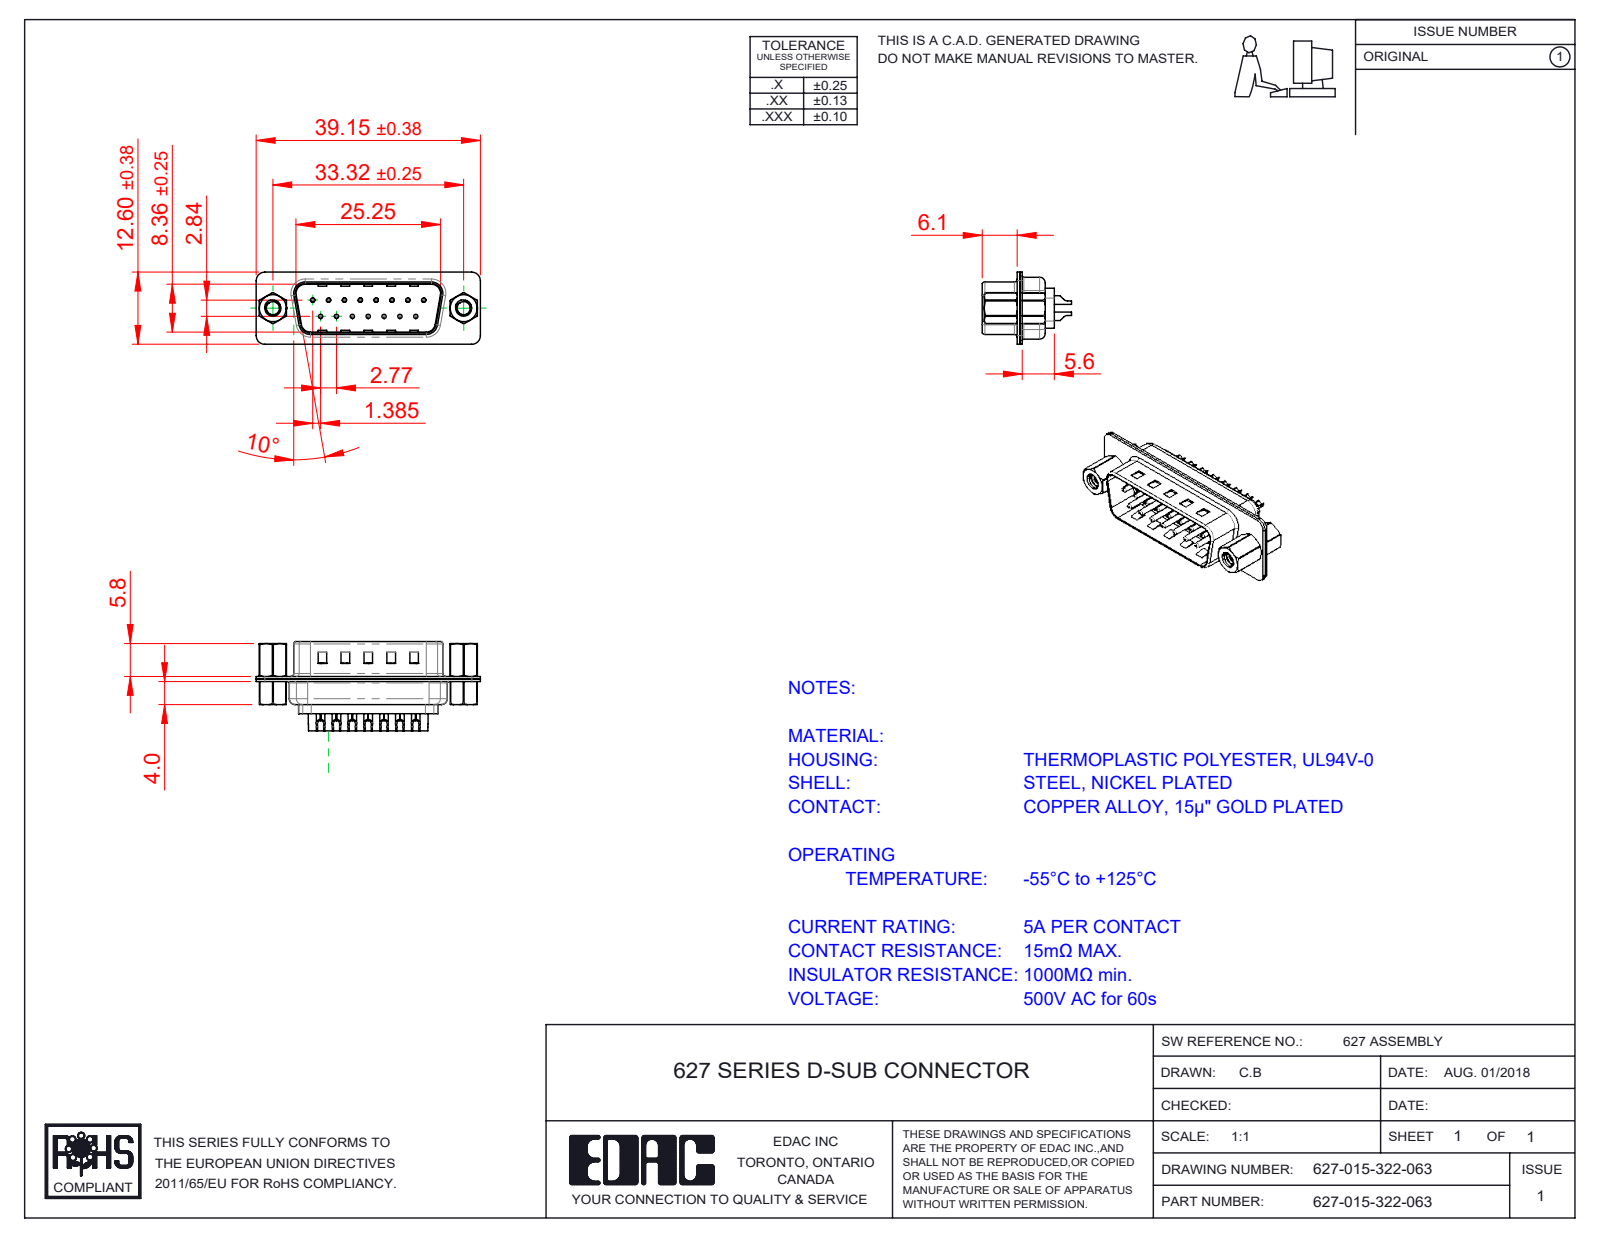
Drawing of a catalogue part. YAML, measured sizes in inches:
part_name: "627-015-322-063; 627 4-40 Threaded Rivet; 627 Contact Row 2_22L; 627 Housing_15 LP (+4 more)"
step_written_by: "SolidWorks 2020 (CONFIG_CONTROL_DESIGN)"
units: inches
bodies: {solids: 22, faces: 1422, planar: 371, cylindrical: 638, other: 413}
overall_size: [1.541, 0.604, 0.496]
volume: 0.125
surface_area: 9.137
round_holes:
  - {diameter: 0.014, count: 15}
  - {diameter: 0.043, count: 15}
  - {diameter: 0.063, count: 15}
  - {diameter: 0.089, count: 2}
  - {diameter: 0.09, count: 2}
  - {diameter: 0.157, count: 2}
  - {diameter: 0.189, count: 2}
round_bosses_or_shafts:
  - {diameter: 0.079, count: 15}
  - {diameter: 0.059, count: 15}
  - {diameter: 0.03, count: 15}
  - {diameter: 0.197, count: 2}
  - {diameter: 0.193, count: 2}
  - {diameter: 0.11, count: 2}
partial_cylinders:
  - {radius: 0.059, count: 16}
  - {radius: 0.079, count: 12}
  - {radius: 0.02, count: 8}
  - {radius: 0.063, count: 8}
  - {radius: 0.039, count: 6}
  - {radius: 0.01, count: 4}
  - {radius: 0.024, count: 4}
  - {radius: 0.026, count: 4}
face_to_face_distances: [0.016, 0.018, 0.035, 0.032, 0.377, 0.345, 0.059, 0.055, 0.256, 0.22]
hole_center_spacings: [0.124, 0.109, 0.218, 0.327, 0.436, 0.198, 0.198, 0.294]
